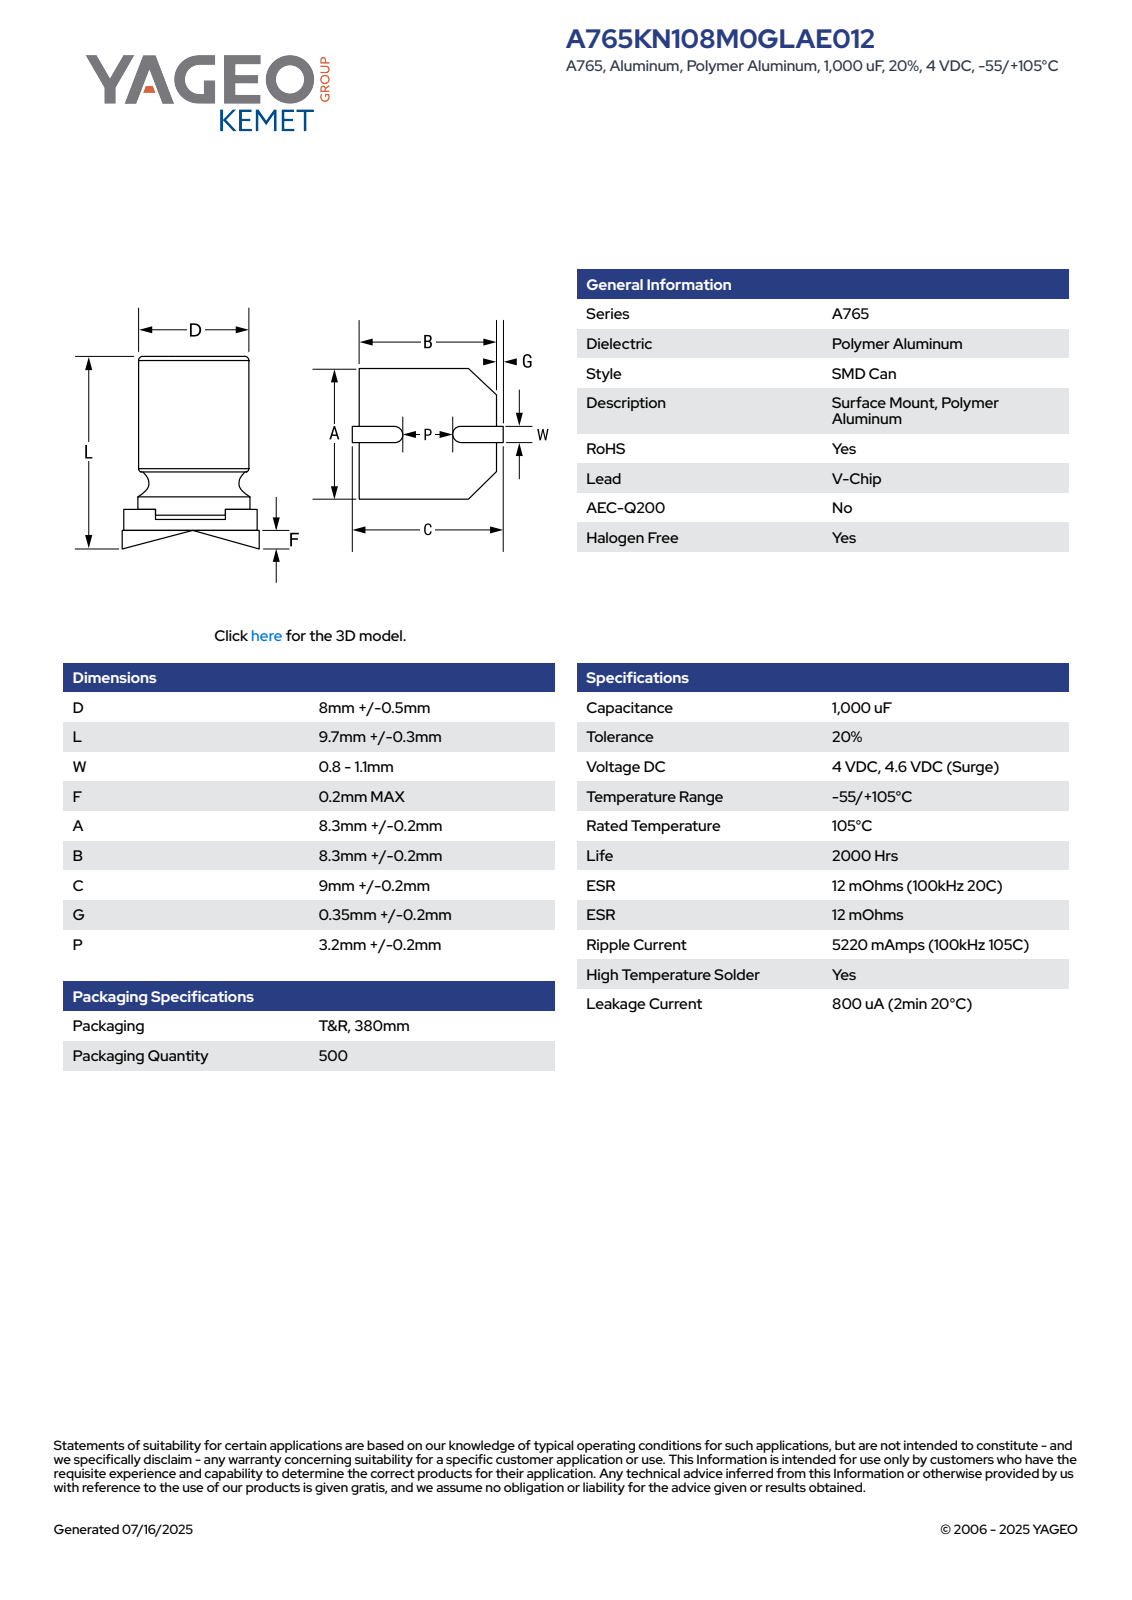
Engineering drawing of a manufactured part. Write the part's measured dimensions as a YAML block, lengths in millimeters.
part_name: "CAC_KS_8X9.7_D8.5L10W1.1F0.2A8.5B8.5C9.2P3.4"
step_written_by: "SolidWorks 2014 (AUTOMOTIVE_DESIGN)"
units: millimeters
bodies: {solids: 5, faces: 76, planar: 59, cylindrical: 11, other: 6}
overall_size: [10.01, 9.2, 8.5]
volume: 528
surface_area: 565
round_bosses_or_shafts:
  - {diameter: 8.13, count: 1}
partial_cylinders:
  - {radius: 0.2, count: 2}
  - {radius: 3.38, count: 1}
  - {radius: 4.25, count: 1}
face_to_face_distances: [0.5, 9.8, 9.3, 9.81, 9.31, 8.5, 2.5, 2, 7.3, 7.31]
